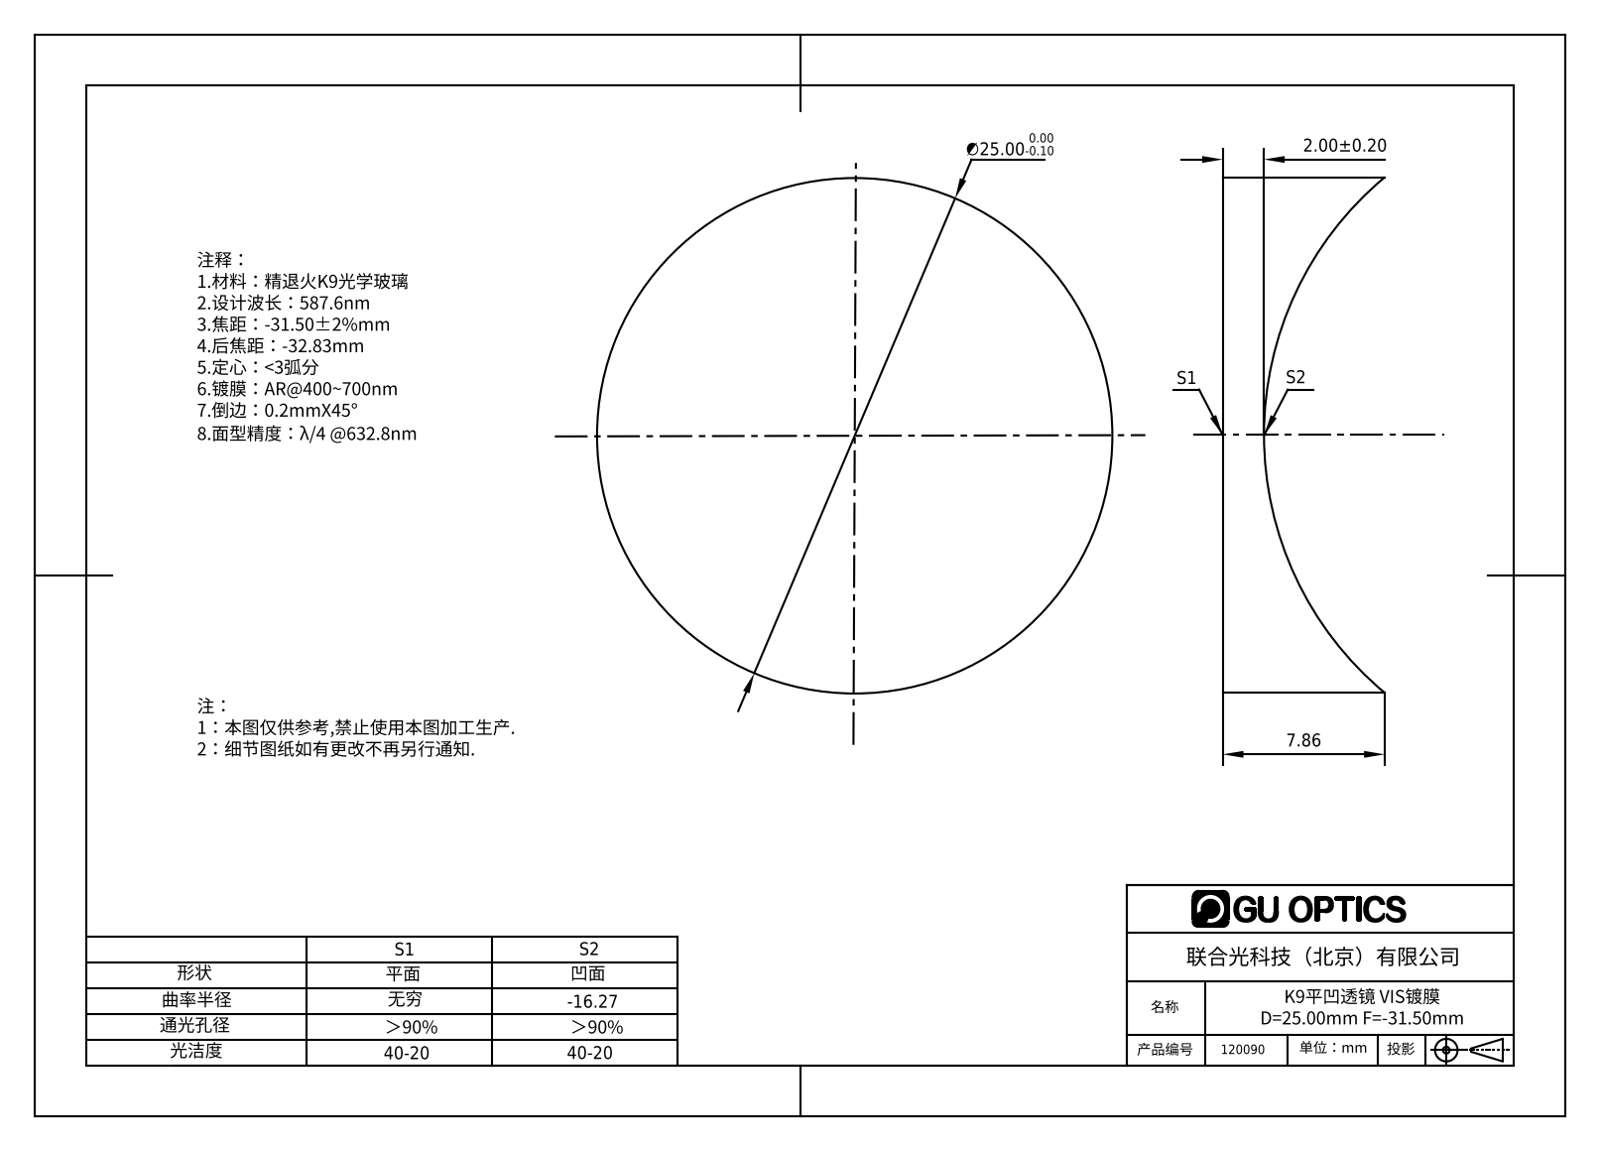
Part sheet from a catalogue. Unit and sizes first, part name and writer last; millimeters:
Units: millimetres
Overall size (bounding box): 25 × 25 × 7.86
Round bosses / shafts (diameter × count): ⌀25 ×1
Volume: 2 314 mm³ · Surface area: 1 706 mm²
Bodies: 1 solid, 5 faces (1 planar, 2 cylindrical, 2 other)
Part name (STEP PRODUCT): 120030
STEP written by: SolidWorks 2016 (AUTOMOTIVE_DESIGN)
